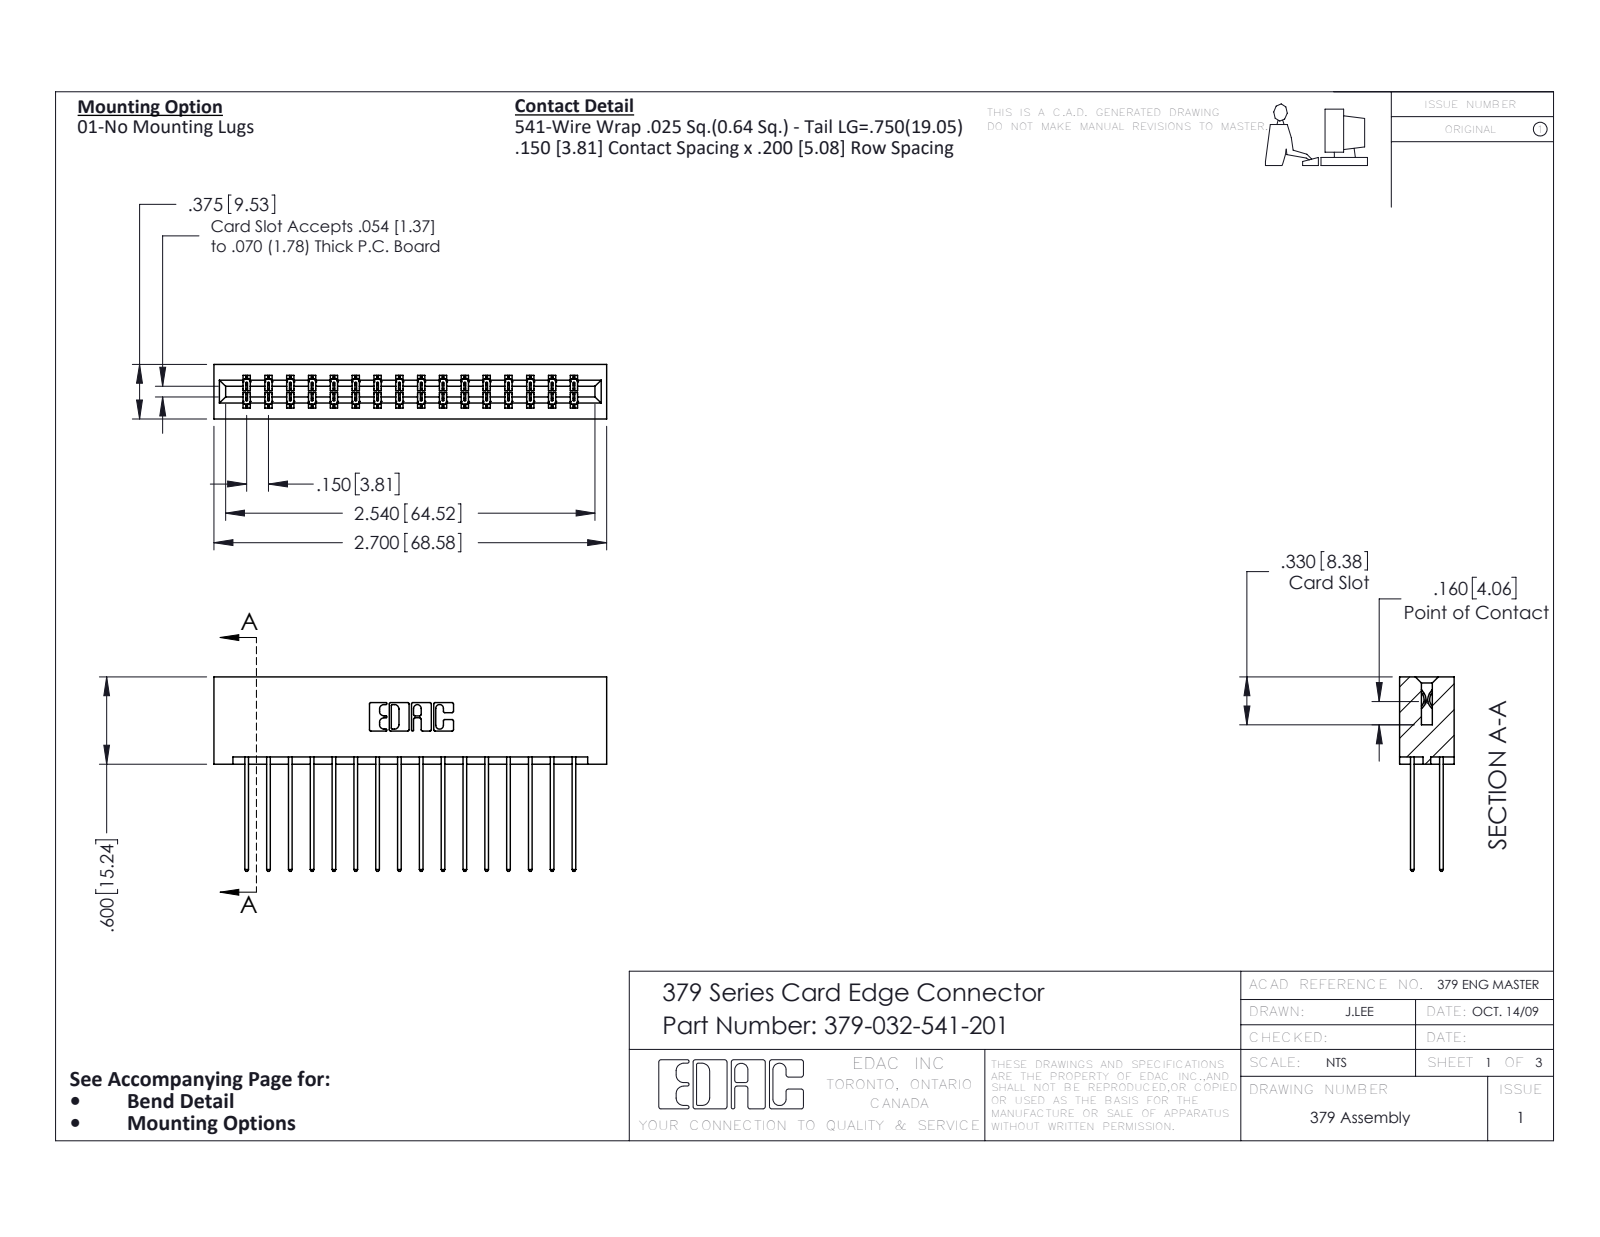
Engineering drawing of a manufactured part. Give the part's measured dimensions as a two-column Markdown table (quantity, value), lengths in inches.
| quantity | value |
| --- | --- |
| part name | 345-292-001_345-293-141; 379-032-541-201; 379 Part_Lugless |
| STEP written by | SolidWorks 2020 (CONFIG_CONTROL_DESIGN) |
| units | inches |
| bodies | 33 solids, 1770 faces (1218 planar, 552 cylindrical, 0 other) |
| overall size | 2.7 × 1.337 × 0.375 |
| volume | 0.482 in³ |
| surface area | 14.88 in² |
| partial cylindrical surfaces (radius × count) | 0.006 × 48, 0.01 × 32, 0.01 × 22, 0.007 × 6, 0.031 × 6, 0.026 × 3, 0.014 × 2, 0.022 × 2 |
| main face-to-face distances | 0.3, 0.075, 0.1, 0.2, 0.375, 0.275, 0.15, 0.025, 0.076, 0.15 |
